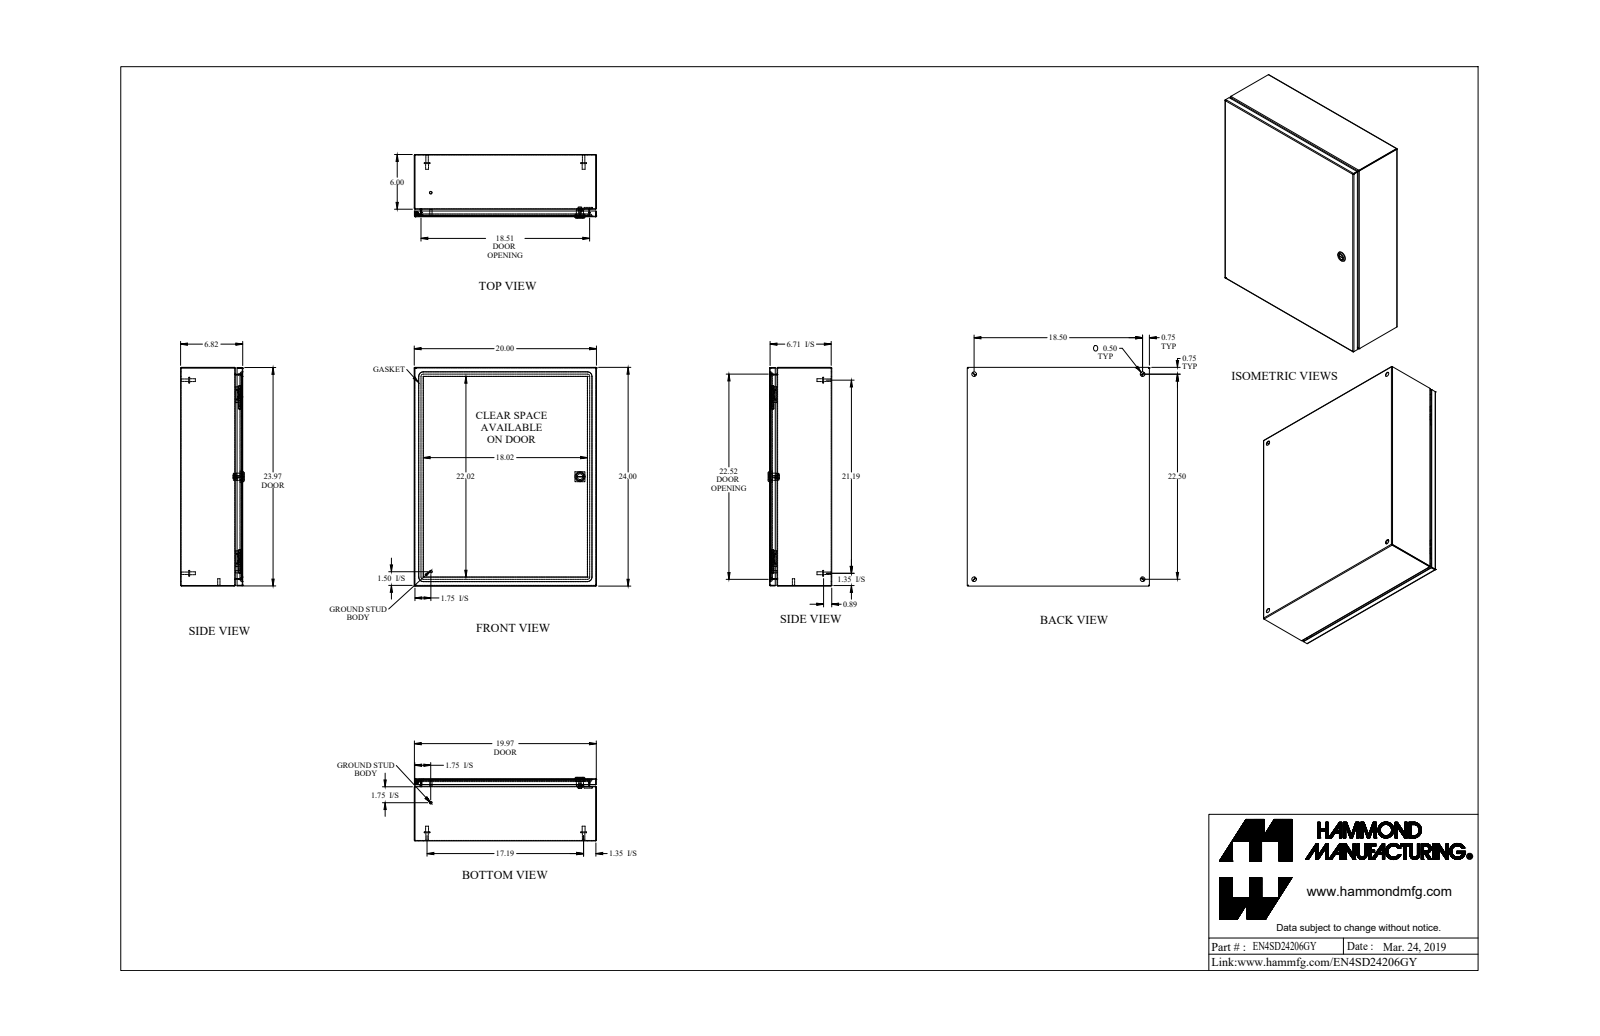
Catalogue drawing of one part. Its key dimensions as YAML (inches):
part_name: "EN4SD24206GY_Default"
step_written_by: "SolidWorks 2019 (CONFIG_CONTROL_DESIGN)"
units: inches
bodies: {solids: 21, faces: 634, planar: 285, cylindrical: 213, other: 136}
overall_size: [24, 20, 6.982]
volume: 103.2
surface_area: 3513
round_holes:
  - {diameter: 0.5, count: 4}
  - {diameter: 0.172, count: 1}
  - {diameter: 0.232, count: 1}
  - {diameter: 0.24, count: 1}
  - {diameter: 0.242, count: 1}
  - {diameter: 0.625, count: 1}
  - {diameter: 0.785, count: 1}
round_bosses_or_shafts:
  - {diameter: 0.625, count: 4}
  - {diameter: 0.313, count: 4}
  - {diameter: 0.27, count: 4}
  - {diameter: 0.281, count: 2}
  - {diameter: 0.25, count: 2}
  - {diameter: 1.1, count: 1}
  - {diameter: 0.525, count: 1}
  - {diameter: 0.455, count: 1}
partial_cylinders:
  - {radius: 0.029, count: 21}
  - {radius: 0.086, count: 21}
  - {radius: 0.25, count: 16}
  - {radius: 19, count: 8}
  - {radius: 0.006, count: 4}
  - {radius: 0.062, count: 4}
  - {radius: 0.499, count: 4}
  - {radius: 0.125, count: 2}
face_to_face_distances: [0.057, 6.765, 6.708, 6.822, 19.943, 23.943, 19.886, 20, 23.886, 24]
hole_center_spacings: [18.5, 22.5, 29.129, 11.299, 11.3, 20.754, 20.755]
